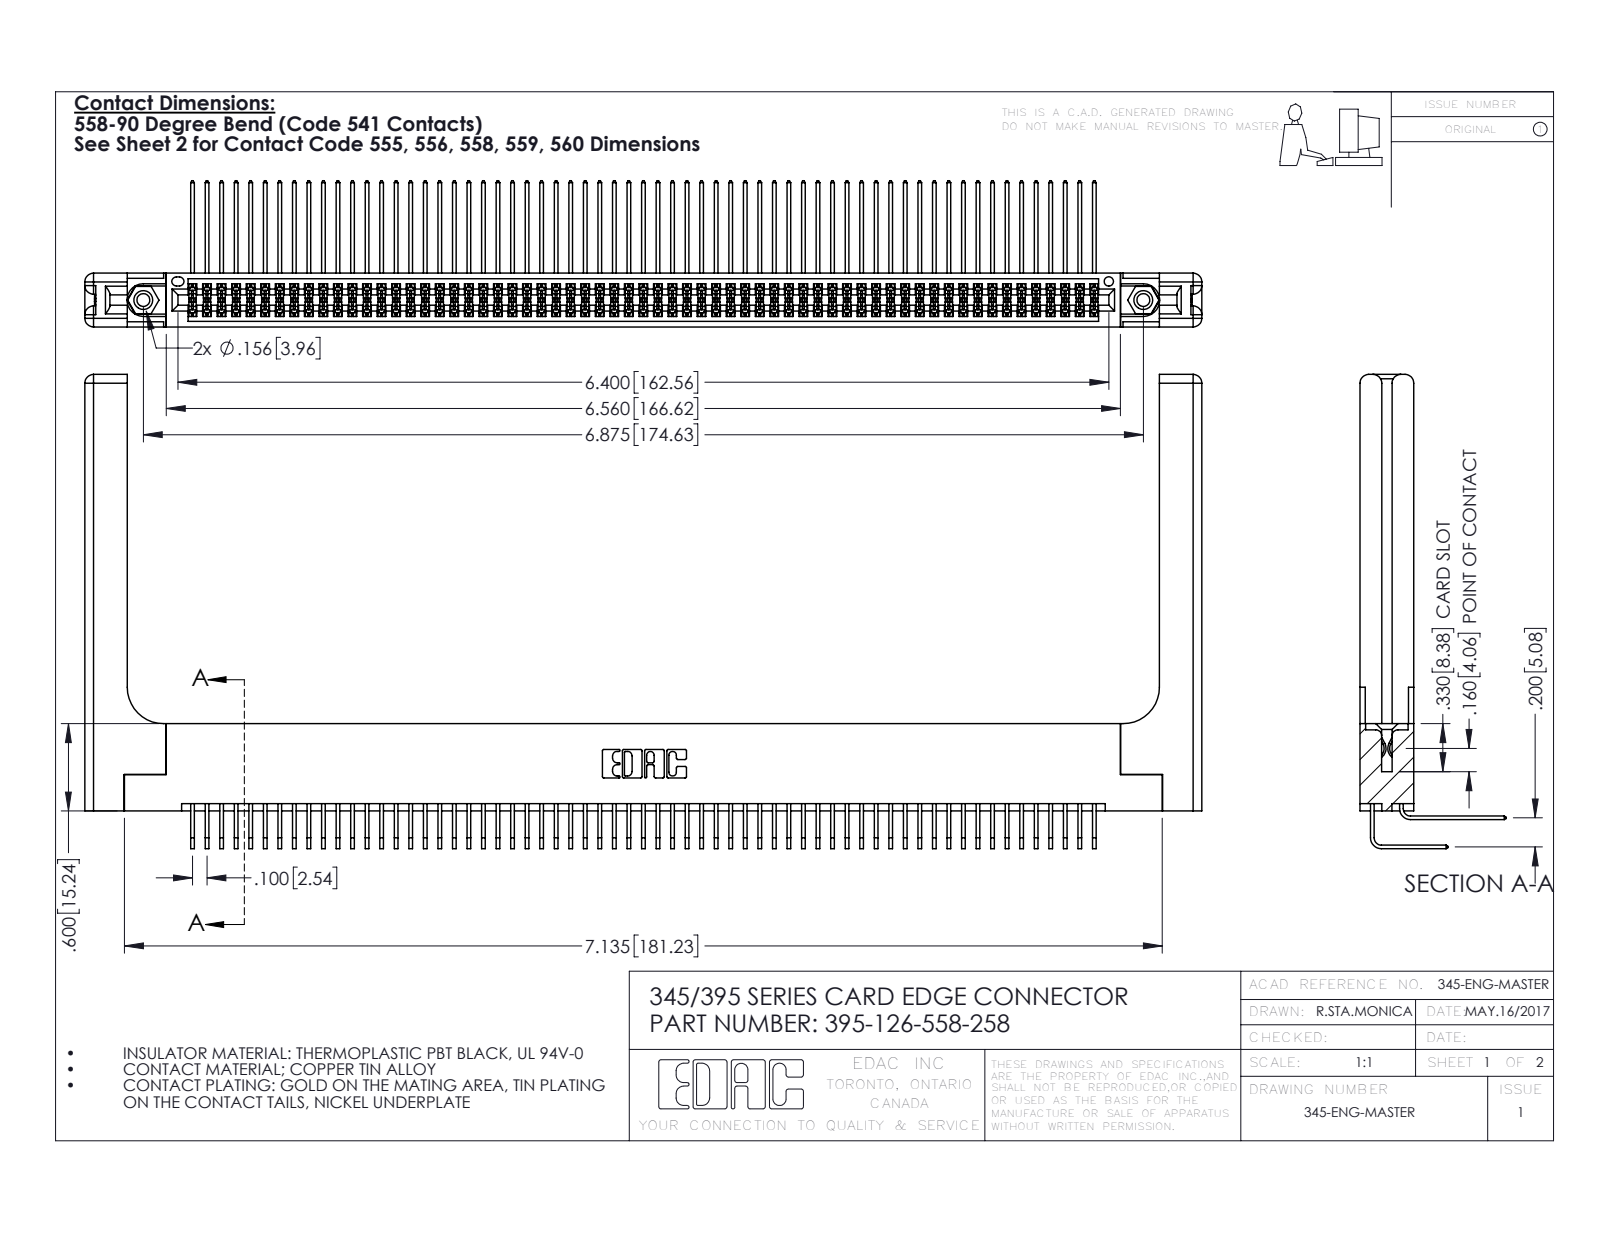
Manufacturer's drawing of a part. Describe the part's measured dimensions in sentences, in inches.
The part is named "345-220-058_345-220-058; 345-250-001_345-250-001-102; 395-126-558-258; 345-292-001_558 Tail - 2 (+2 more)". Its 3-D file was written by "SolidWorks 2016 (CONFIG_CONTROL_DESIGN)". It is 131 solids with 6934 faces: 4638 planar, 2236 cylindrical and 60 other. Overall it measures 7.679 by 3.259 by 1.005 inches. Its volume is 1.73 cubic inches and its surface area 59.29 square inches. Round holes: 2 of diameter 0.089, 2 of diameter 0.125, 2 of diameter 0.156, 1 of diameter 0.064. Round bosses or shafts: 2 of diameter 0.155. Partial cylindrical surfaces (rounded edges, fillets, slot ends): 190 of radius 0.006, 22 of radius 0.01, 16 of radius 0.06, 6 of radius 0.007, 6 of radius 0.031, 3 of radius 0.026, 2 of radius 0.014, 2 of radius 0.019. The main face-to-face distances are 0.072, 0.298, 0.2, 0.37, 0.098, 0.272, 0.025, 0.225, 0.025, 0.148. The hole center spacings are 0.27, 6.639, 6.875.
